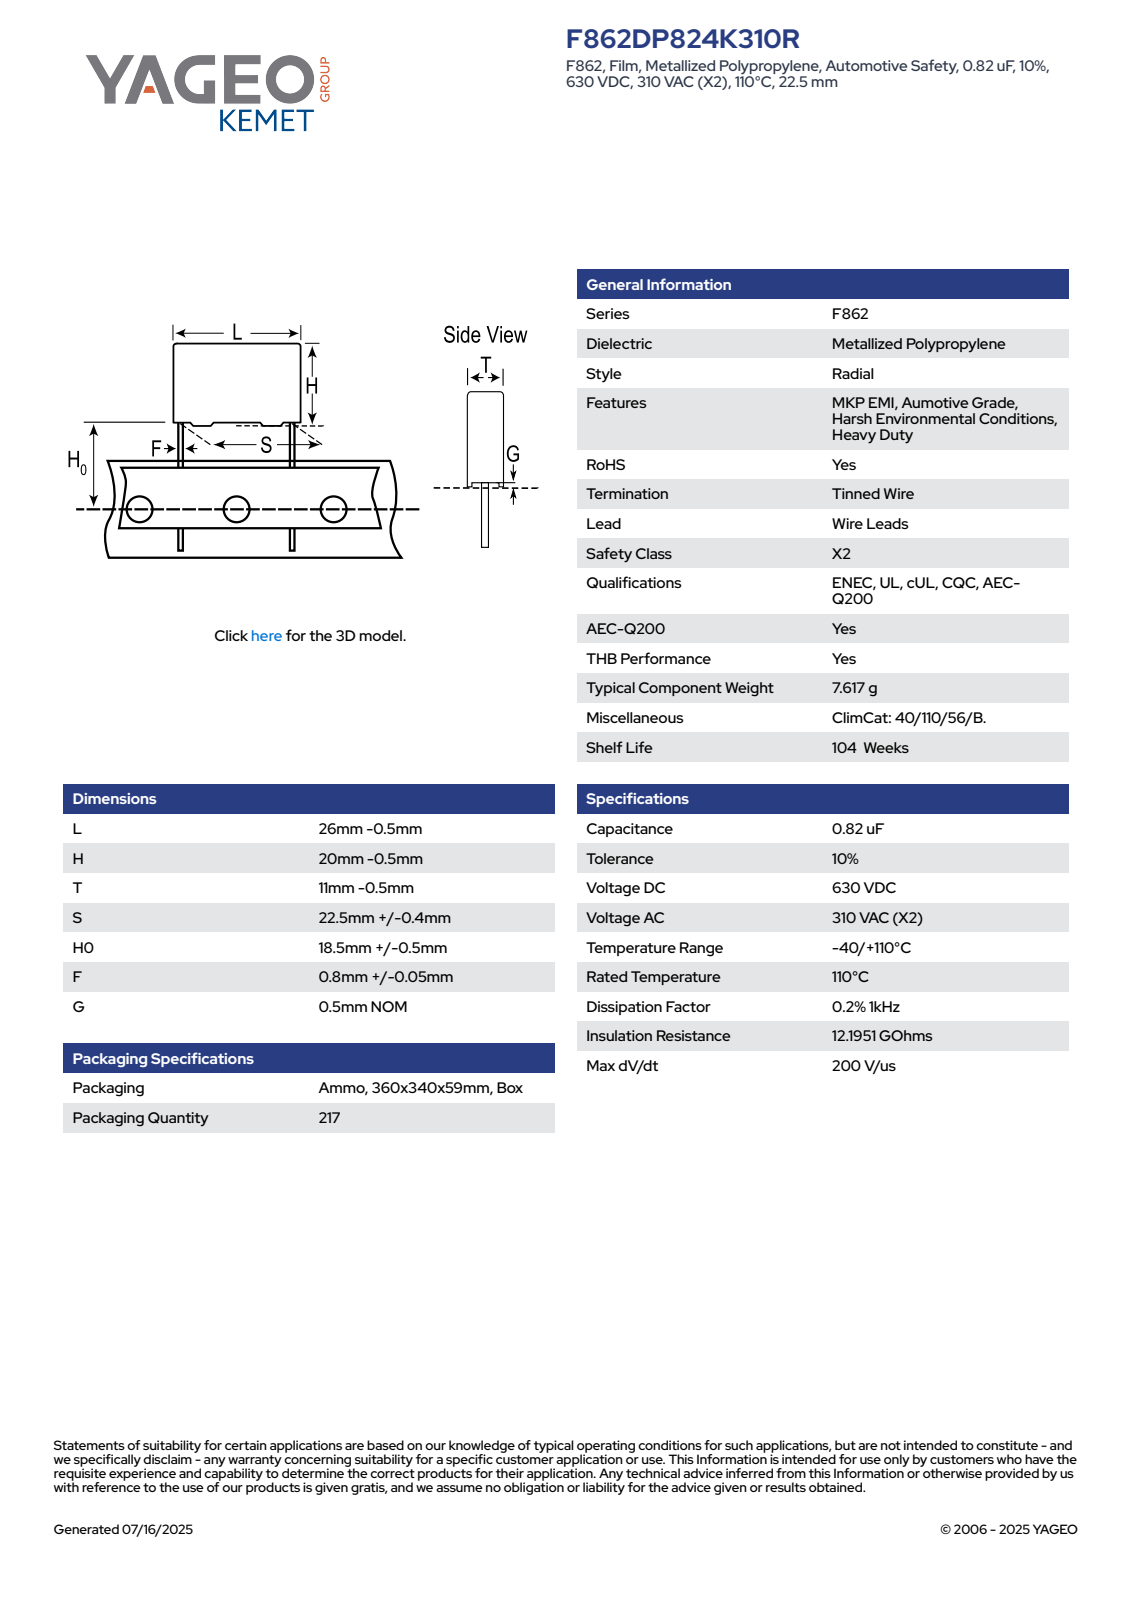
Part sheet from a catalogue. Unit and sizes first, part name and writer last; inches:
Units: inches
Overall size (bounding box): 1.516 × 1.004 × 0.414
Round bosses / shafts (diameter × count): ⌀0.033 ×2
Partial cylindrical surfaces — rounded edges, fillets, slot ends (radius × count): R0.02 ×4
Main face-to-face distances: 0.413, 0.748, 1.004, 0.414, 0.768, 0.02, 0.024, 0.39, 0.024, 0.366
Volume: 0.312 in³ · Surface area: 3.224 in²
Bodies: 4 solids, 89 faces (81 planar, 8 cylindrical, 0 other)
Part name (STEP PRODUCT): CFR_RBG_26X20X11_L25.5H19.5T10.5S22.5H019F0.85G0.5
STEP written by: SolidWorks 2014 (AUTOMOTIVE_DESIGN)
